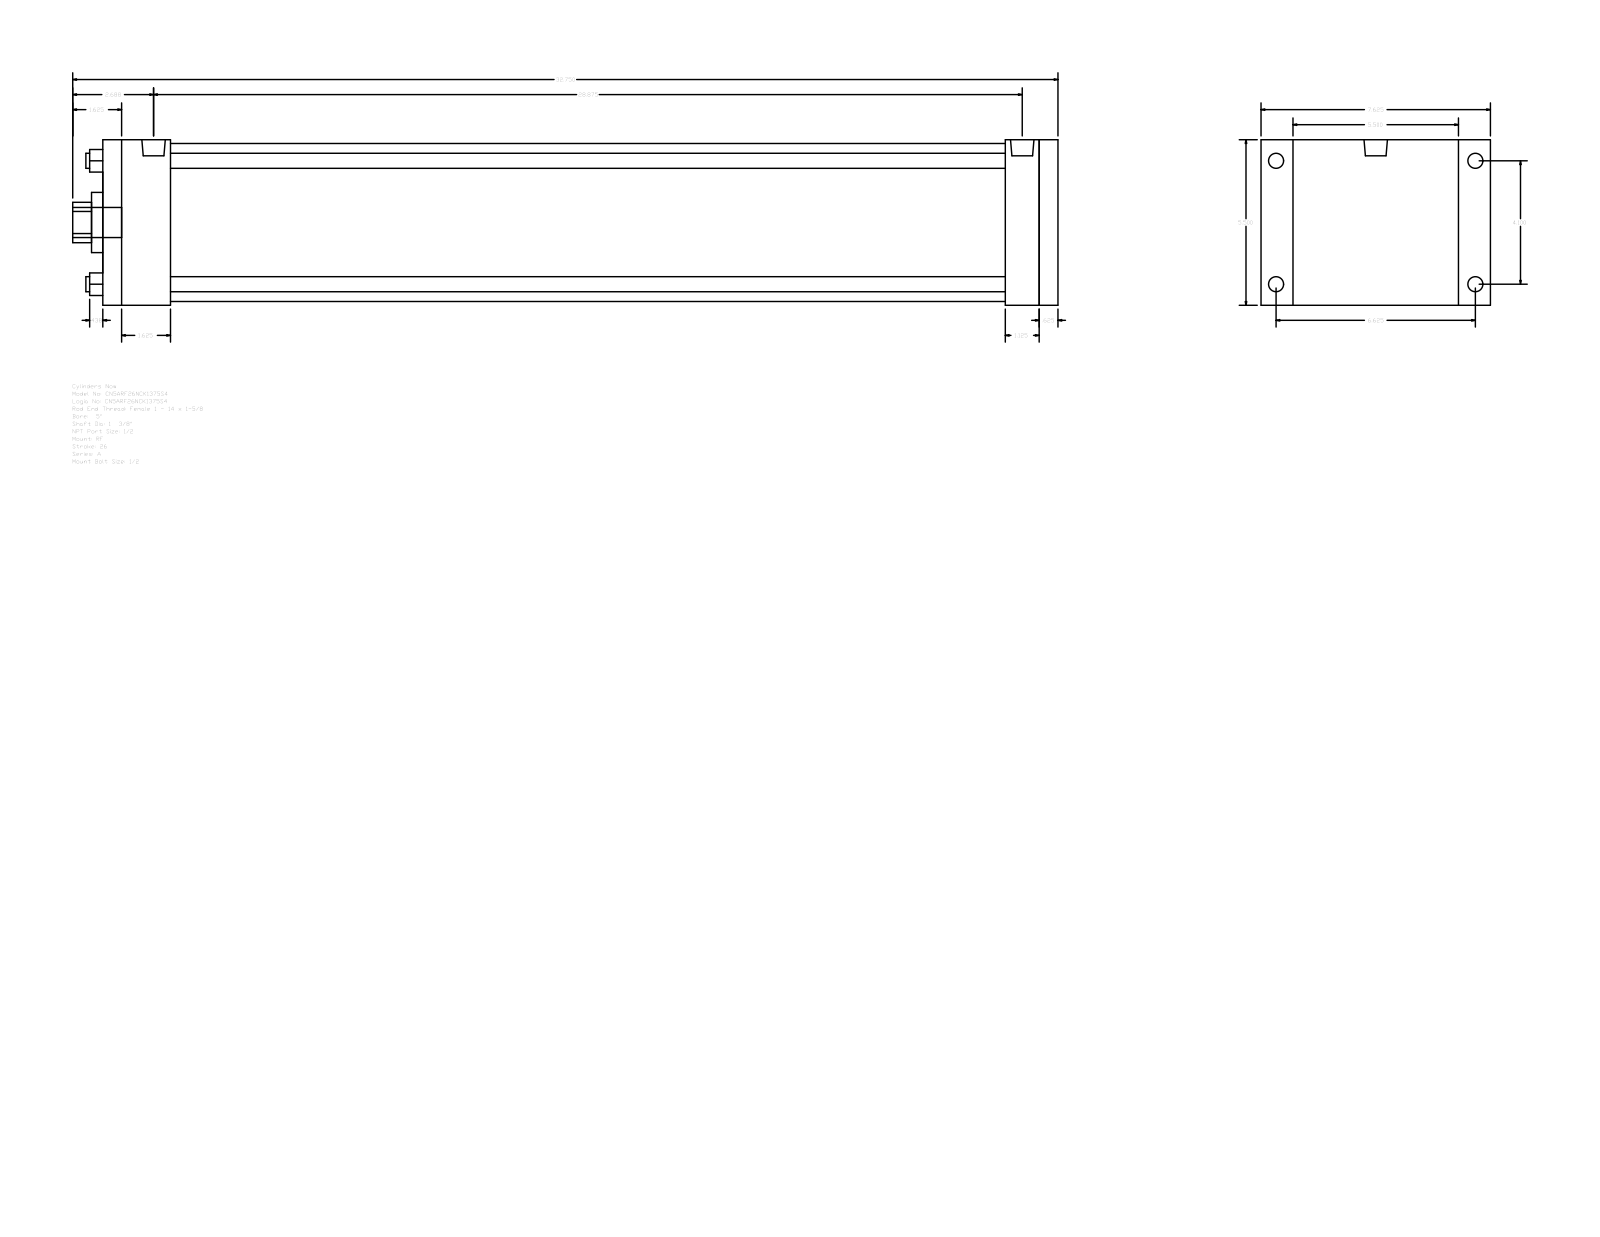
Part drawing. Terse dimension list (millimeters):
name: A_RF__0500_1.375
written by: GSSL Pune (CONFIG_CONTROL_DESIGN)
unit: mm
bodies: 0 solids, 92 faces (64 planar, 28 cylindrical, 0 other)
size: 831.85 × 193.68 × 139.7
holes: 4× ⌀12.7, 1× ⌀34.92, 1× ⌀50.8, 1× ⌀133.35
bosses: 4× ⌀12.7, 4× ⌀8.73, 2× ⌀19.77, 1× ⌀25.4
rounds: 1× R17.06
face distances: 139.7, 806.45, 15.87, 790.58, 28.58, 57.15, 733.43, 749.3, 762, 704.85
hole spacings: 73.64, 104.14, 147.28
